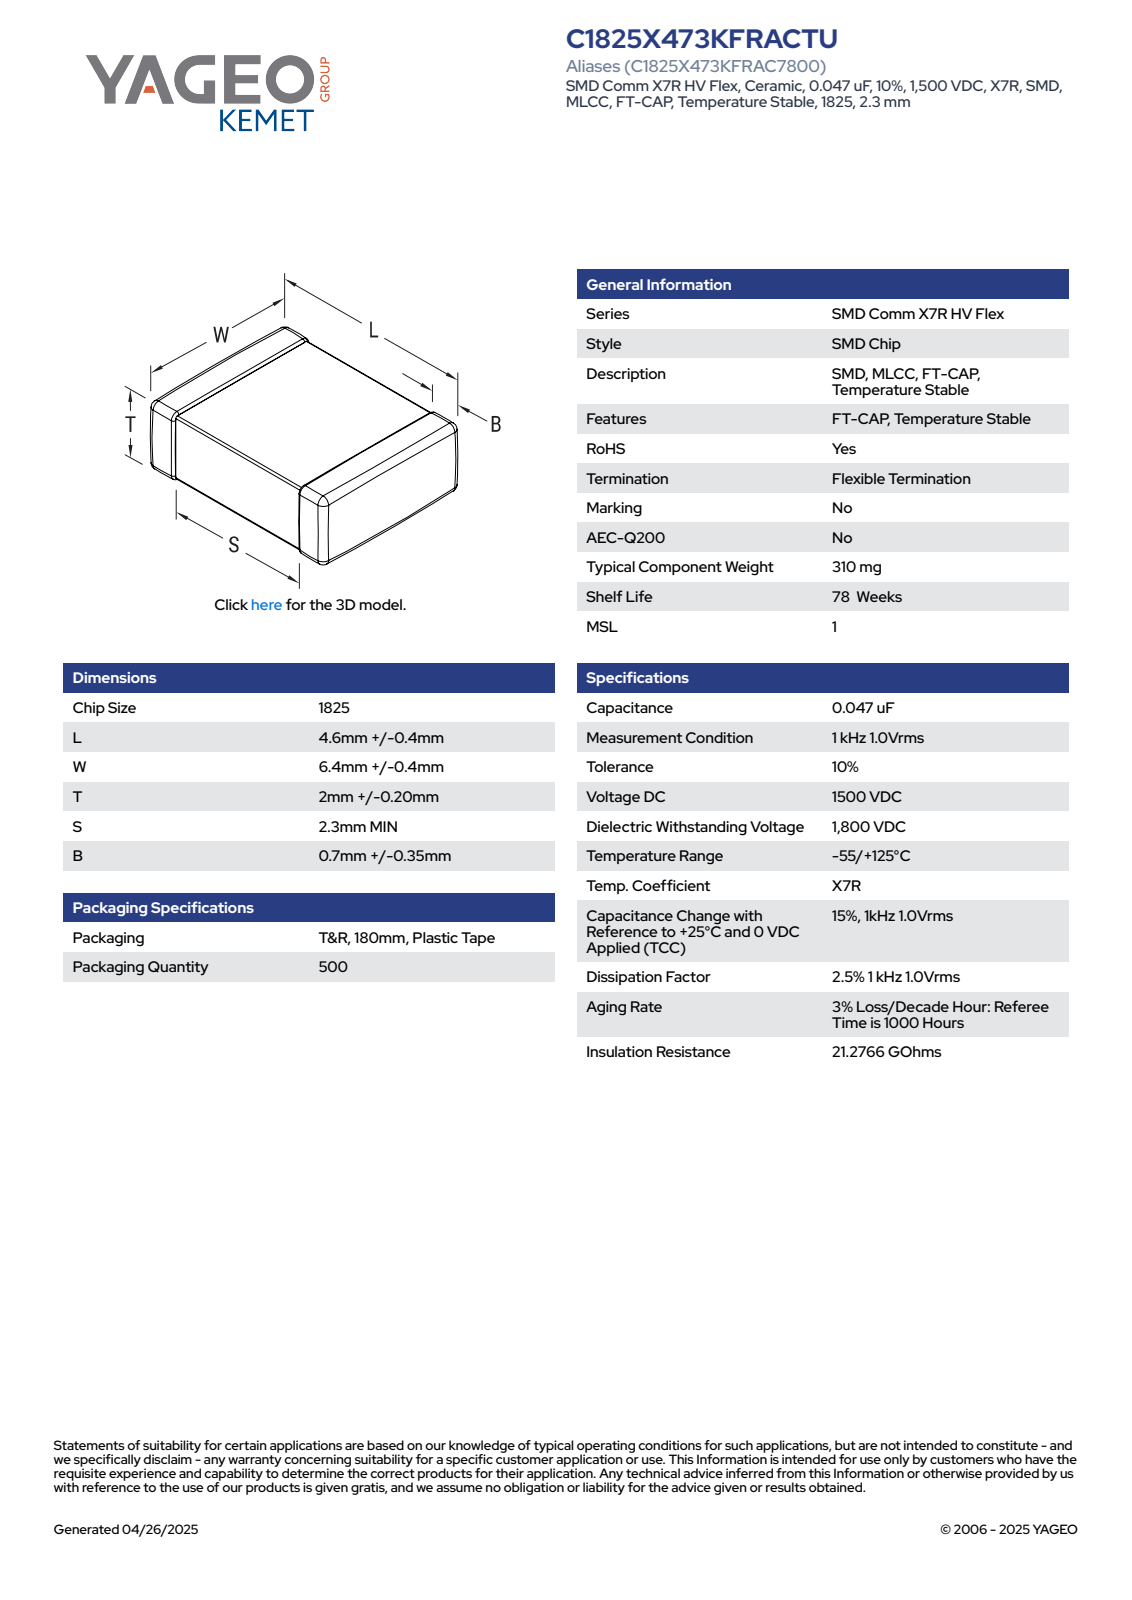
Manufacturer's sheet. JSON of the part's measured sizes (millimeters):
{"part_name": "CCS_CCSTDNOS_1825_L5W6.8T2.2B1.05", "step_written_by": "SolidWorks 2014 (AUTOMOTIVE_DESIGN)", "units": "millimeters", "bodies": {"solids": 4, "faces": 121, "planar": 71, "cylindrical": 34, "other": 16}, "overall_size": [6.8, 5, 2.2], "volume_mm3": 67, "surface_area_mm2": 117, "partial_cylinders_radius": [[0.14, 24]], "face_to_face_distances": [2.06, 1.92, 5, 2.2, 6.66, 6.52, 6.8, 3.54, 3.12, 0.36]}
